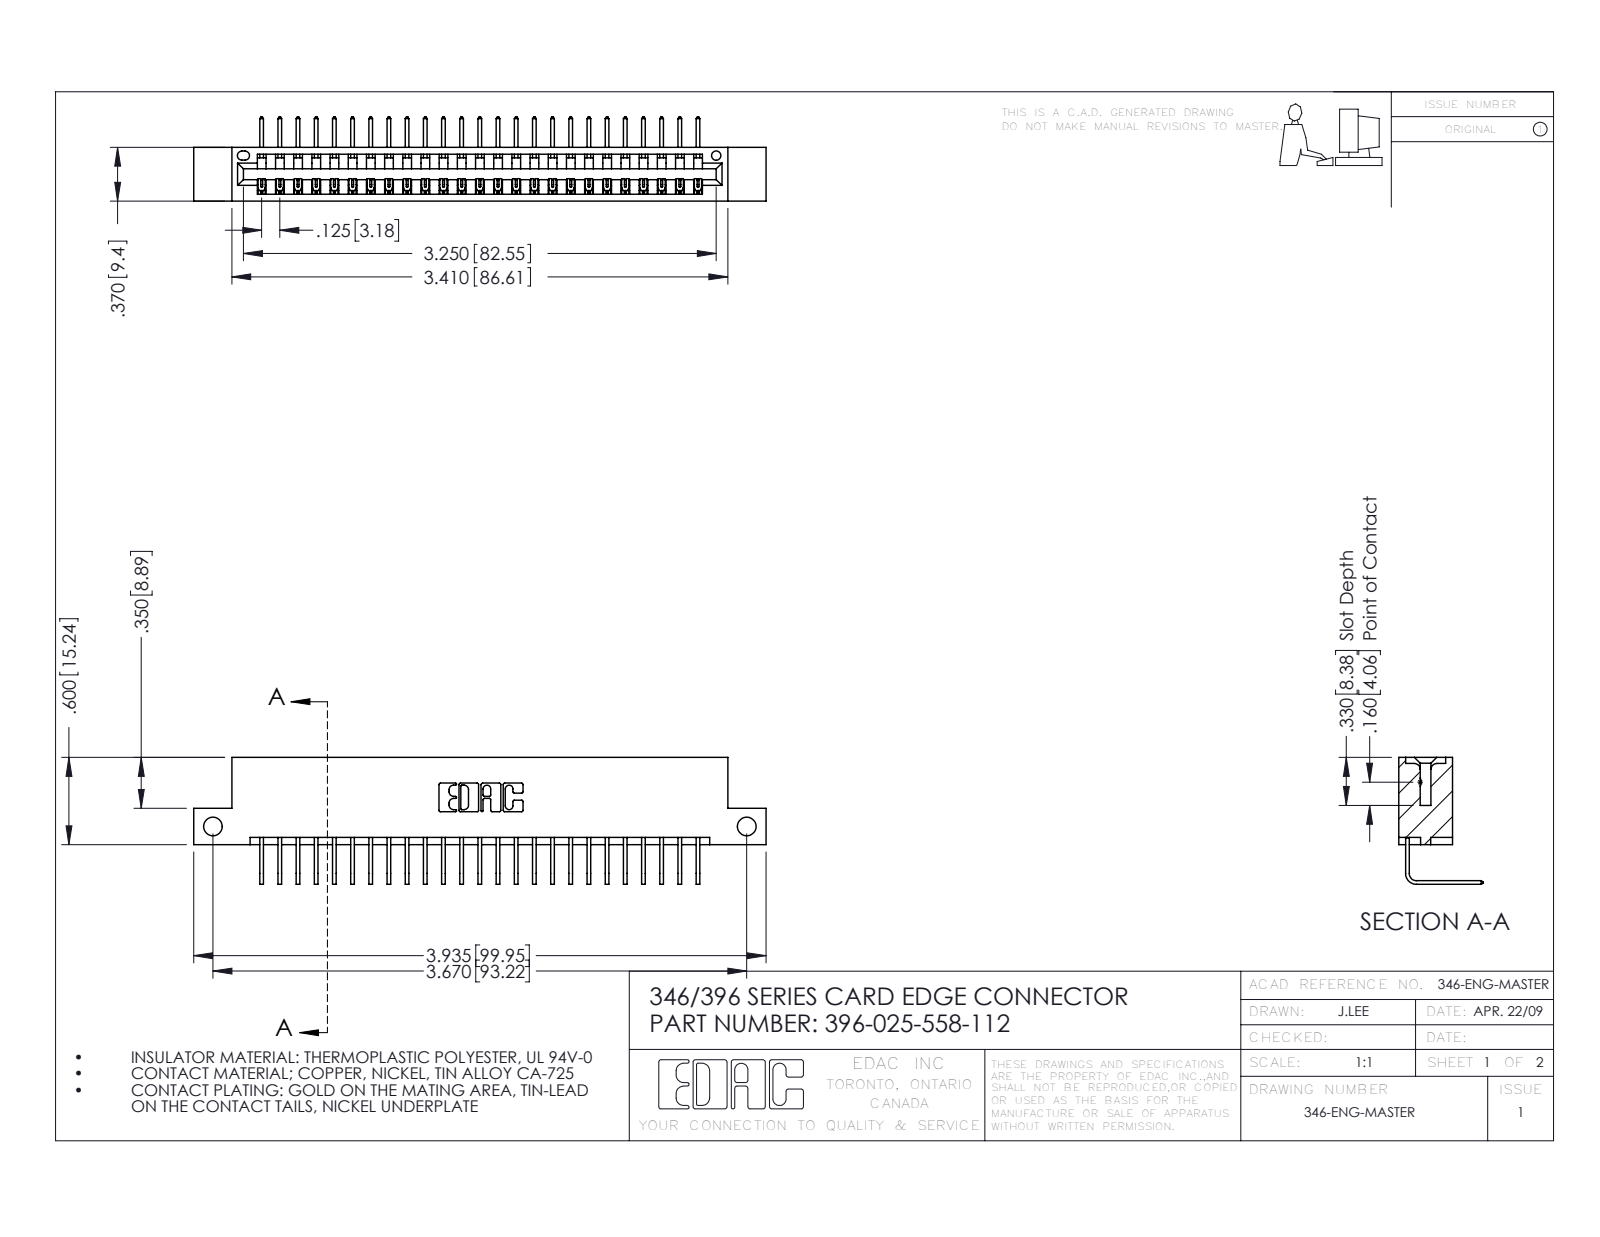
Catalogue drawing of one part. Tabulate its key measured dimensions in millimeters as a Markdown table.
| quantity | value |
| --- | --- |
| part name | 396-025-558-112; 346 Part_Flush Mounting Lugs - Side Mount; 345-292-001_558 Tail - 2 |
| STEP written by | SolidWorks 2016 (CONFIG_CONTROL_DESIGN) |
| units | millimeters |
| bodies | 26 solids, 1622 faces (1126 planar, 496 cylindrical, 0 other) |
| overall size | 99.9 × 22.2 × 14.7 |
| volume | 9 440 mm³ |
| surface area | 11 970 mm² |
| round holes (diameter × count) | 3.3 × 2, 1.6 × 1 |
| partial cylindrical surfaces (radius × count) | 0.2 × 50, 0.3 × 22, 0.2 × 6, 0.8 × 6, 0.7 × 3, 0.8 × 2, 1 × 2, 0.4 × 1 |
| main face-to-face distances | 8.2, 1.2, 9.4, 6.4, 7.6, 0.6, 1.8, 3.8, 5.6, 2.5 |
| hole center spacings | 93.2 |
